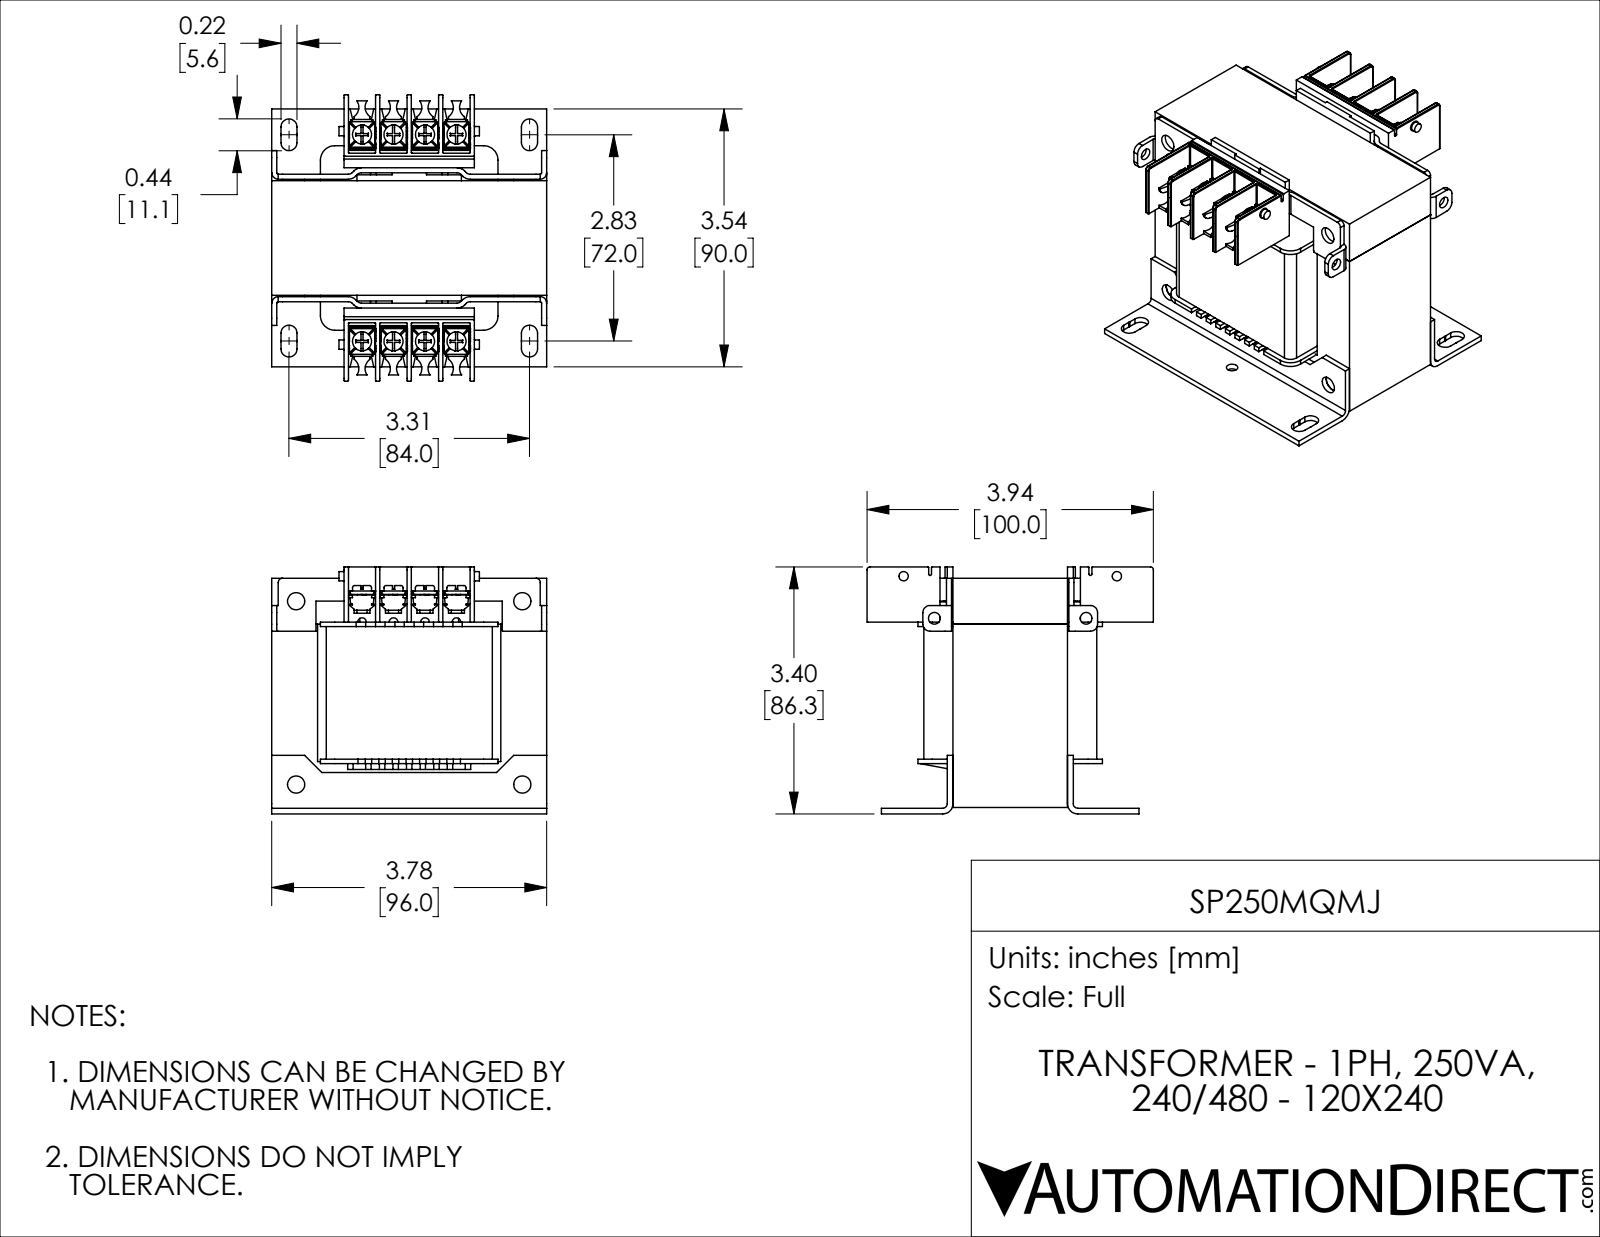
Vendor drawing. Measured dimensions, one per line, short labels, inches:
name: SP250MQMJ
written by: SolidWorks 2018 (AUTOMOTIVE_DESIGN)
unit: in
bodies: 41 solids, 3218 faces (1990 planar, 930 cylindrical, 298 other)
size: 3.937 × 3.78 × 3.396
volume: 24.65 in³; area: 181.7 in²
holes: 10× ⌀0.157, 8× ⌀0.105, 8× ⌀0.138, 4× ⌀0.236, 2× ⌀0.161
bosses: 8× ⌀0.262, 8× ⌀0.24, 8× ⌀0.168, 8× ⌀0.11, 2× ⌀0.128
rounds: 62× R0.01, 52× R0.005, 42× R0.012, 32× R0.029, 16× R0.157, 12× R0.035, 12× R0.065, 10× R0.079
face distances: 0.63, 2.52, 1.575, 3.15, 0.079, 1.772, 1.26, 0.059, 1.89, 0.748
hole spacings: 0.433, 0.866, 2.866, 1.299, 2.833, 2.962, 2.856, 2.875
